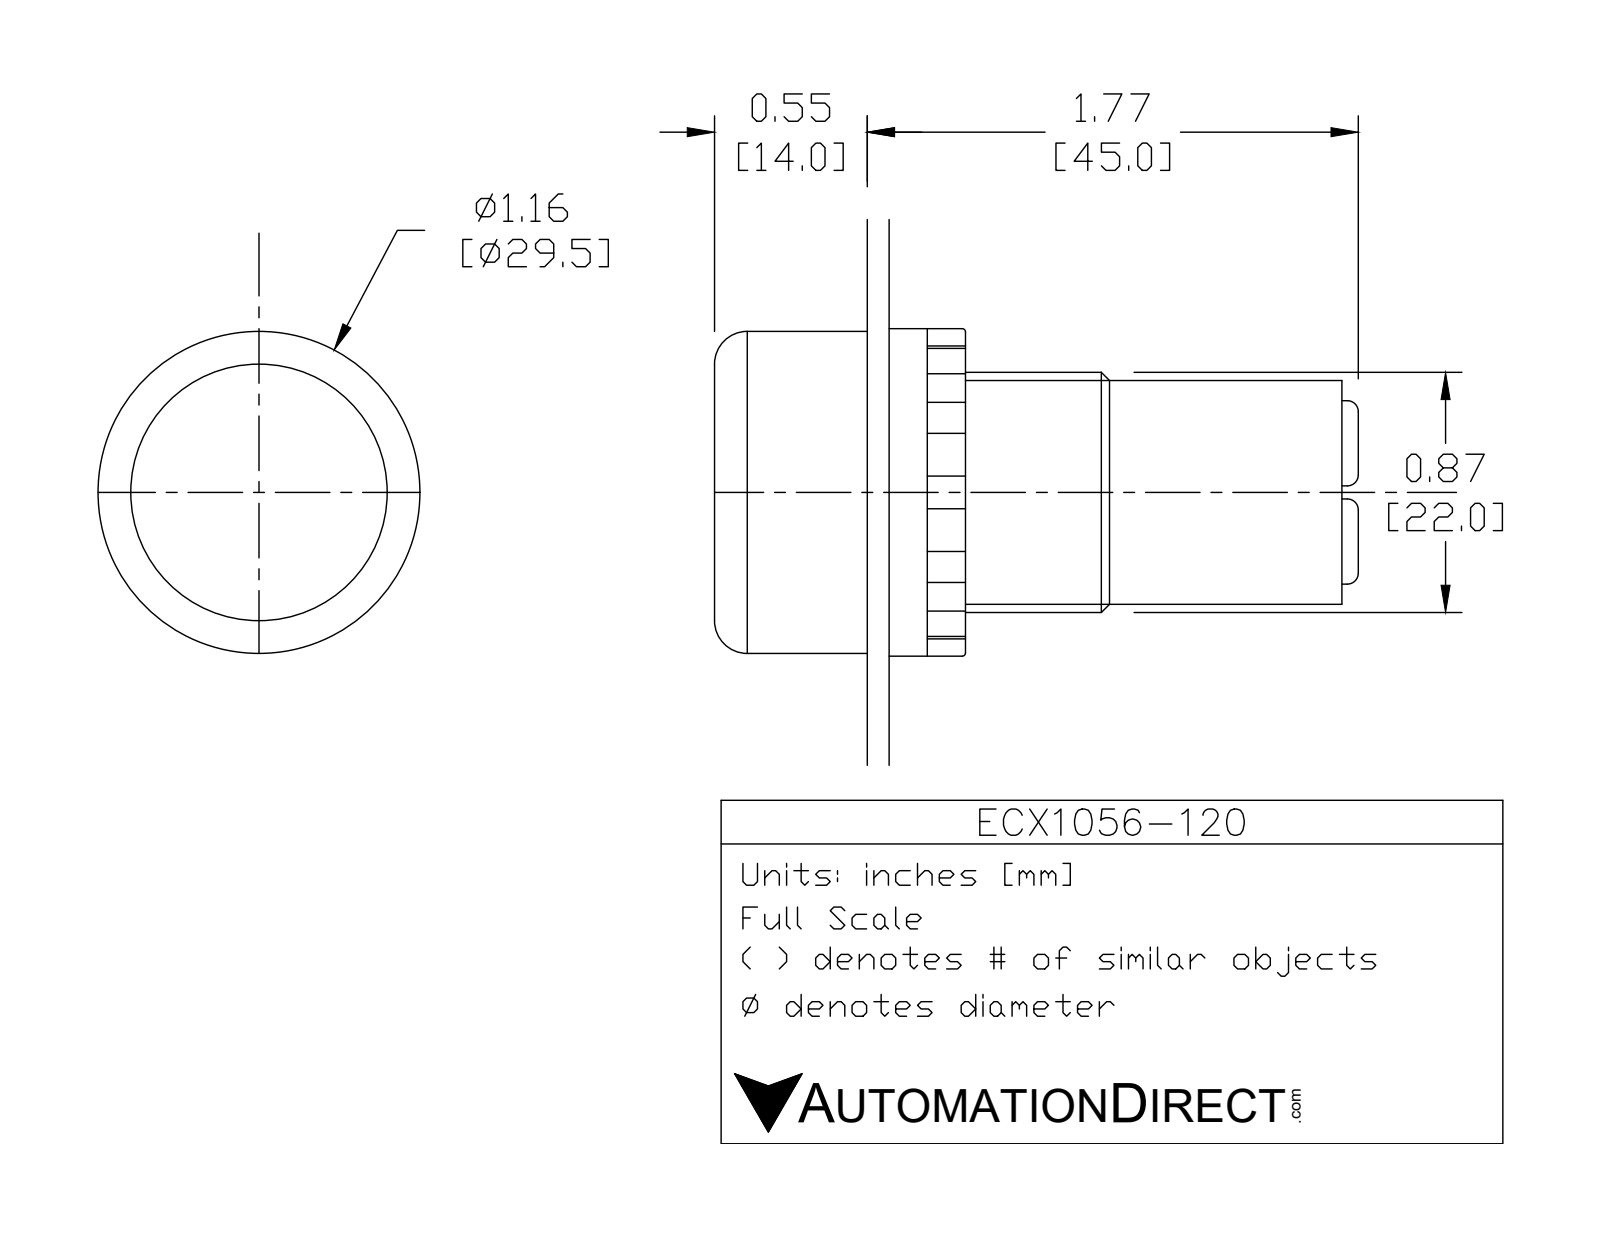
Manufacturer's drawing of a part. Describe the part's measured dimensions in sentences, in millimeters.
The part is named "ECX1056-120". Its 3-D file was written by "SolidWorks 2017 (AUTOMOTIVE_DESIGN)". It is 6 solids with 125 faces: 63 planar, 41 cylindrical and 21 other. Overall it measures 59 by 30 by 30 millimeters. Its volume is 26 294 cubic millimeters and its surface area 9 700 square millimeters. Round holes: 2 of diameter 5.5, 1 of diameter 22.5. Round bosses or shafts: 2 of diameter 4, 1 of diameter 30, 1 of diameter 29, 1 of diameter 26.5, 1 of diameter 22, 1 of diameter 20. Partial cylindrical surfaces (rounded edges, fillets, slot ends): 12 of radius 1, 1 of radius 9. The main face-to-face distances are 13.5, 0.5, 14, 20, 6, 6.5, 39, 7, 13, 27. The hole center spacings are 4.62, 9.24.
